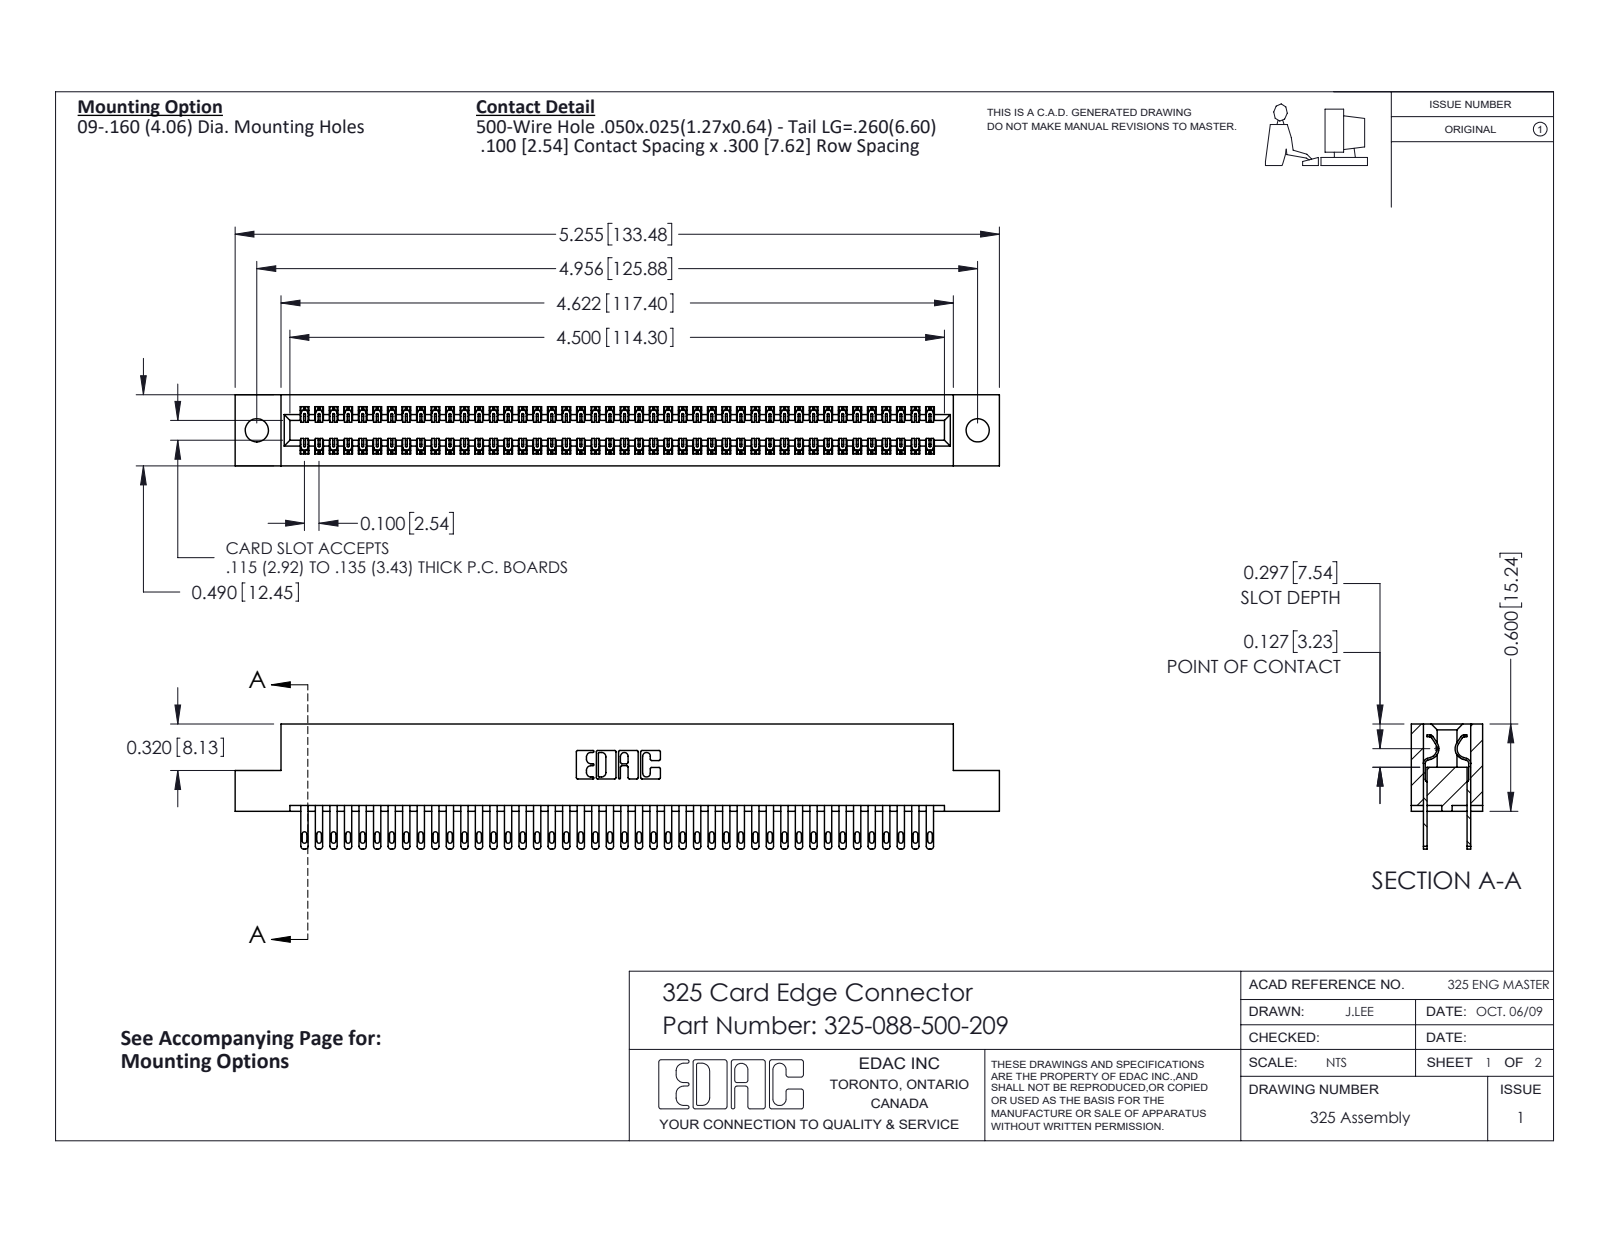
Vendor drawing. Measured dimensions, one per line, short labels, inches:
name: 325-088-500-209; 325-292-001_325-293-100; 325 Part_.160 TH
written by: SolidWorks 2016 (CONFIG_CONTROL_DESIGN)
unit: in
bodies: 89 solids, 4338 faces (2710 planar, 1628 cylindrical, 0 other)
size: 5.255 × 0.86 × 0.49
volume: 1.055 in³; area: 33.81 in²
holes: 2× ⌀0.16
rounds: 132× R0.006, 88× R0.016, 88× R0.02, 22× R0.01, 6× R0.007, 6× R0.031, 3× R0.026, 2× R0.014
face distances: 0.083, 0.407, 0.3, 0.107, 0.383, 0.025, 0.49, 0.325, 0.275, 0.56
hole spacings: 4.956
